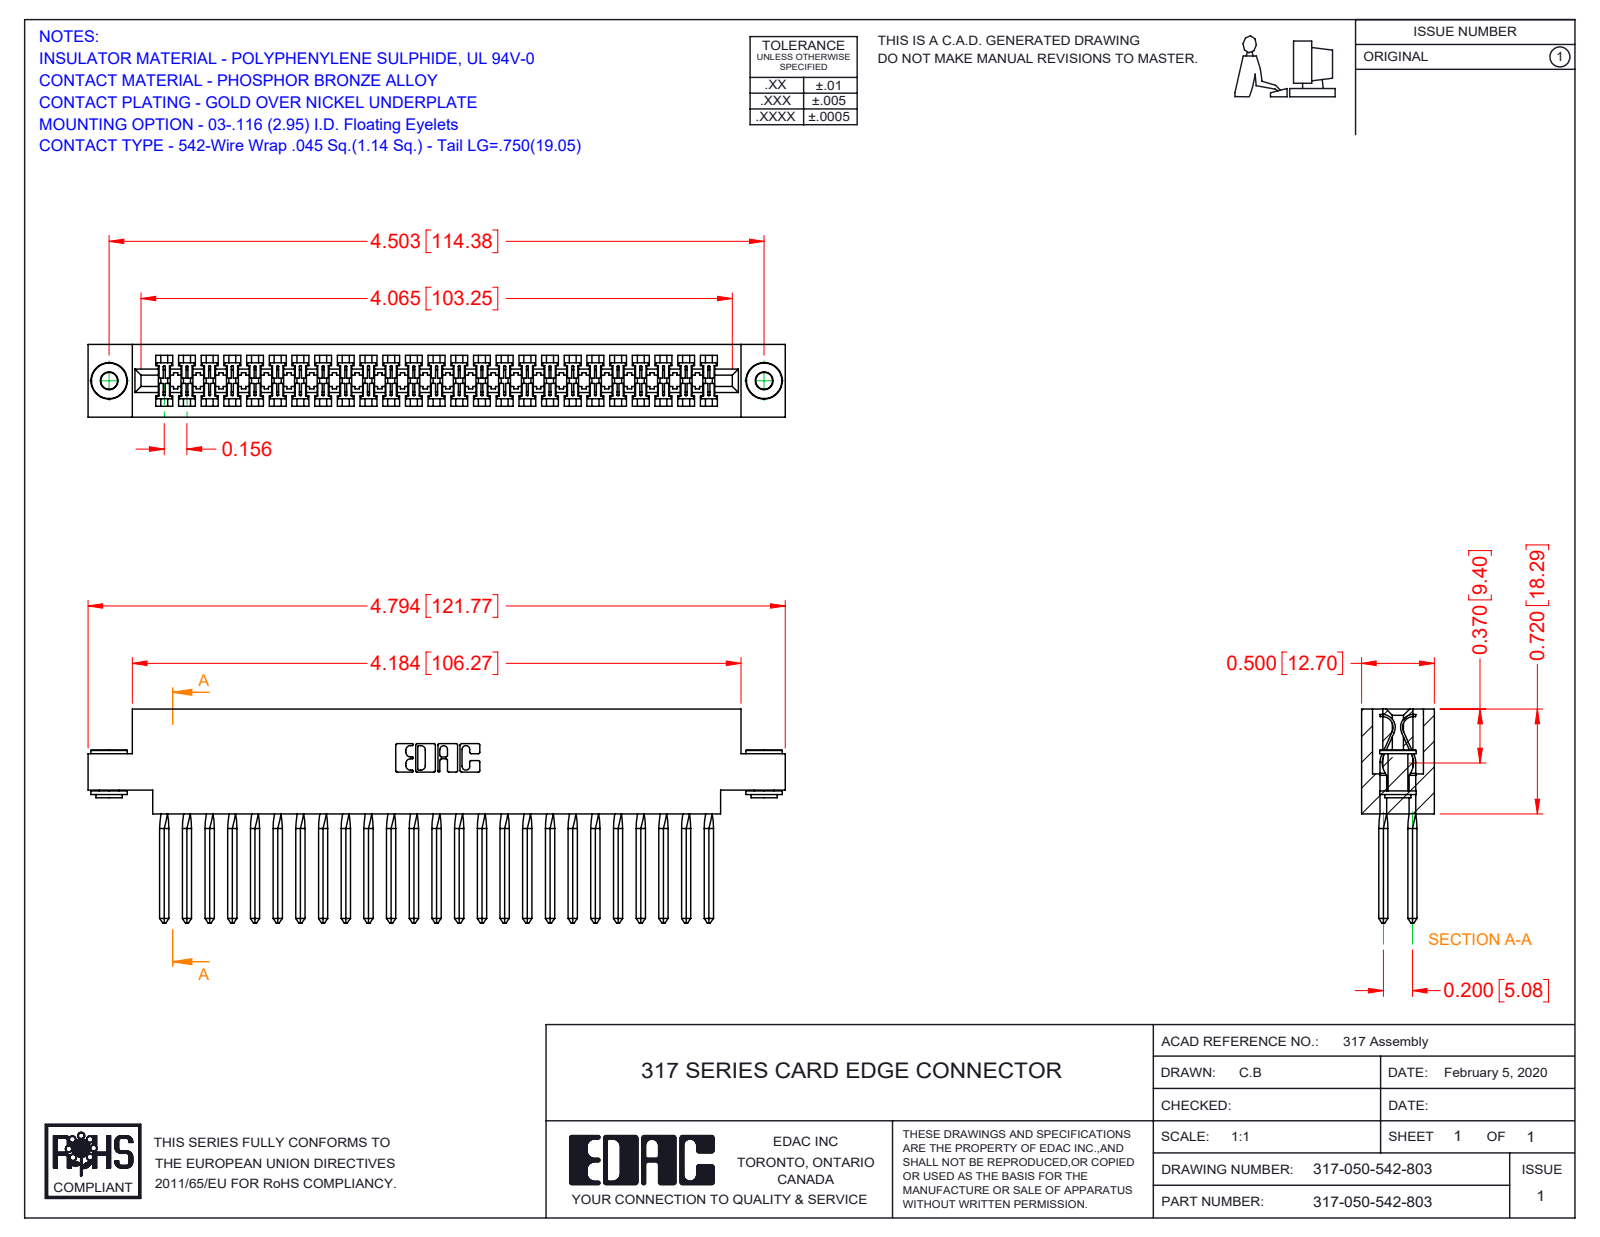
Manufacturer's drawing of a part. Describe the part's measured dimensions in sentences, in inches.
The part is named "317 Part_.156 Dia - TH; 317-050-542-803; 345-250-002_345-250-002-102; 317-290-003_542". Its 3-D file was written by "SolidWorks 2016 (CONFIG_CONTROL_DESIGN)". It is 53 solids with 2990 faces: 2368 planar, 414 cylindrical and 208 other. Overall it measures 4.794 by 1.47 by 0.5 inches. Its volume is 1.185 cubic inches and its surface area 41.35 square inches. Round holes: 2 of diameter 0.116, 2 of diameter 0.156. Round bosses or shafts: 2 of diameter 0.25, 2 of diameter 0.18, 2 of diameter 0.136. Partial cylindrical surfaces (rounded edges, fillets, slot ends): 100 of radius 0.006, 22 of radius 0.01, 6 of radius 0.007, 6 of radius 0.031, 3 of radius 0.026, 2 of radius 0.074, 2 of radius 0.089, 2 of radius 0.1. The main face-to-face distances are 0.5, 0.075, 0.425, 0.35, 0.2, 0.11, 0.116, 0.046, 0.136, 0.72. The hole center spacings are 4.503.
